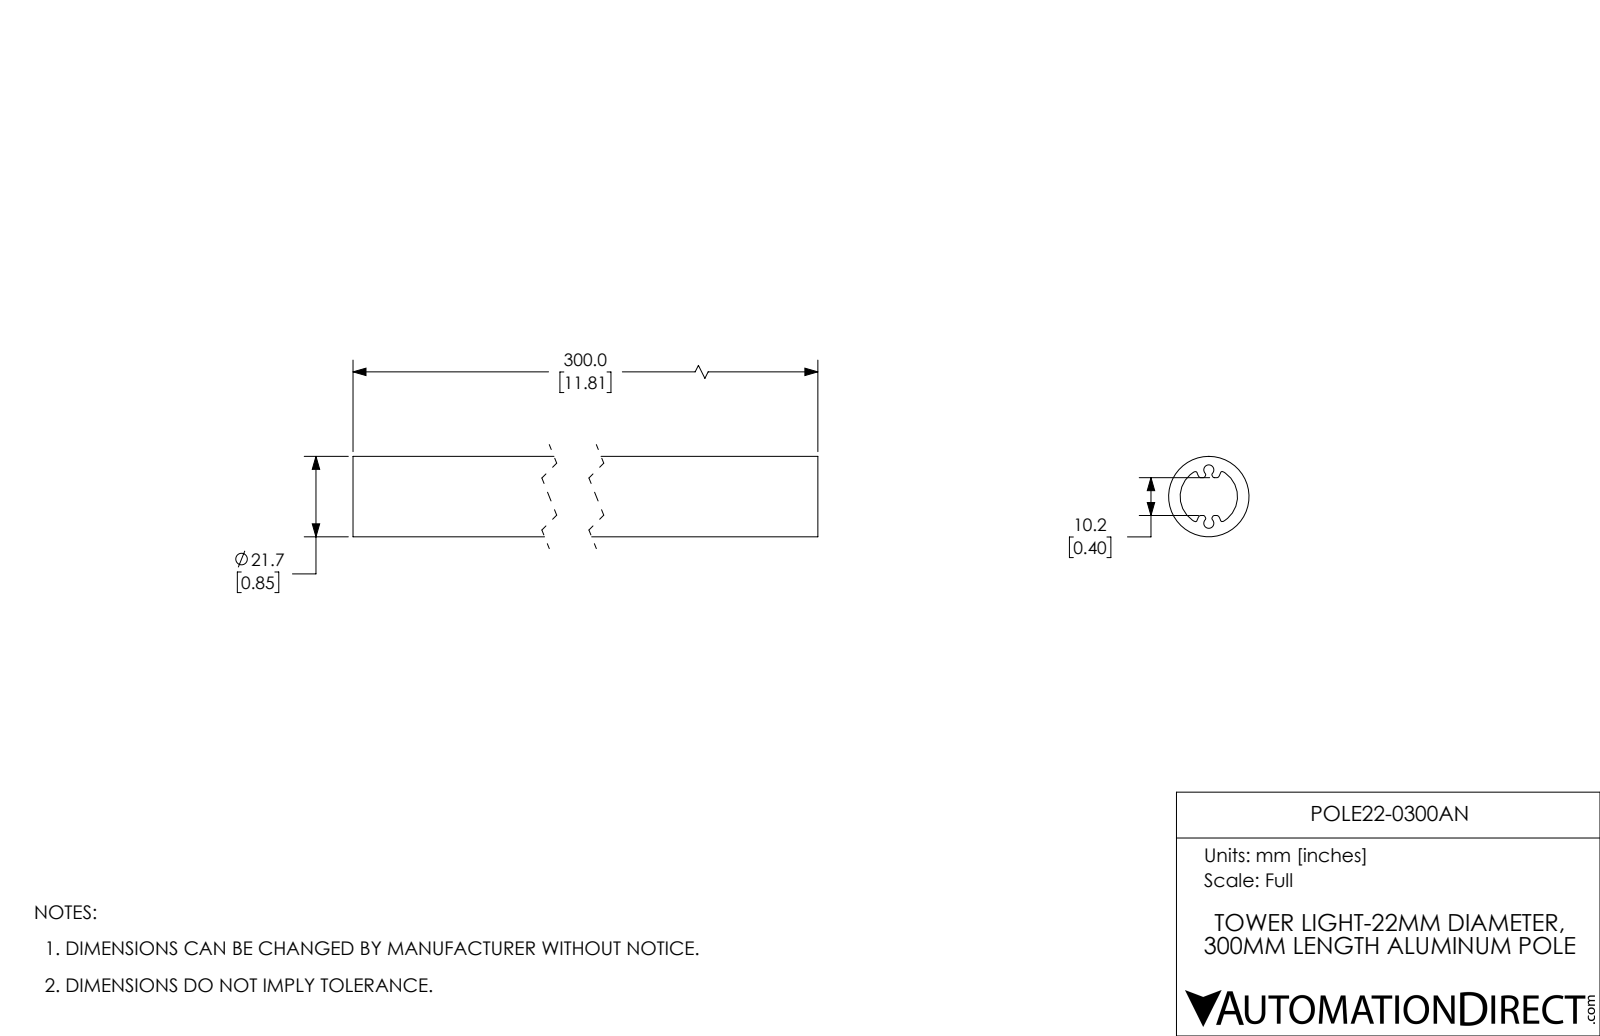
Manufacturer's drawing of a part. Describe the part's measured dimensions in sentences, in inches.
The part is named "POLE22-0300AN". Its 3-D file was written by "SolidWorks 2017 (AUTOMOTIVE_DESIGN)". It is 1 solid with 8 faces: 2 planar, 2 cylindrical and 4 other. Overall it measures 11.811 by 0.854 by 0.854 inches. Its volume is 3.586 cubic inches and its surface area 62.38 square inches. Round bosses or shafts: 1 of diameter 0.854. The main face-to-face distances are 11.811.
